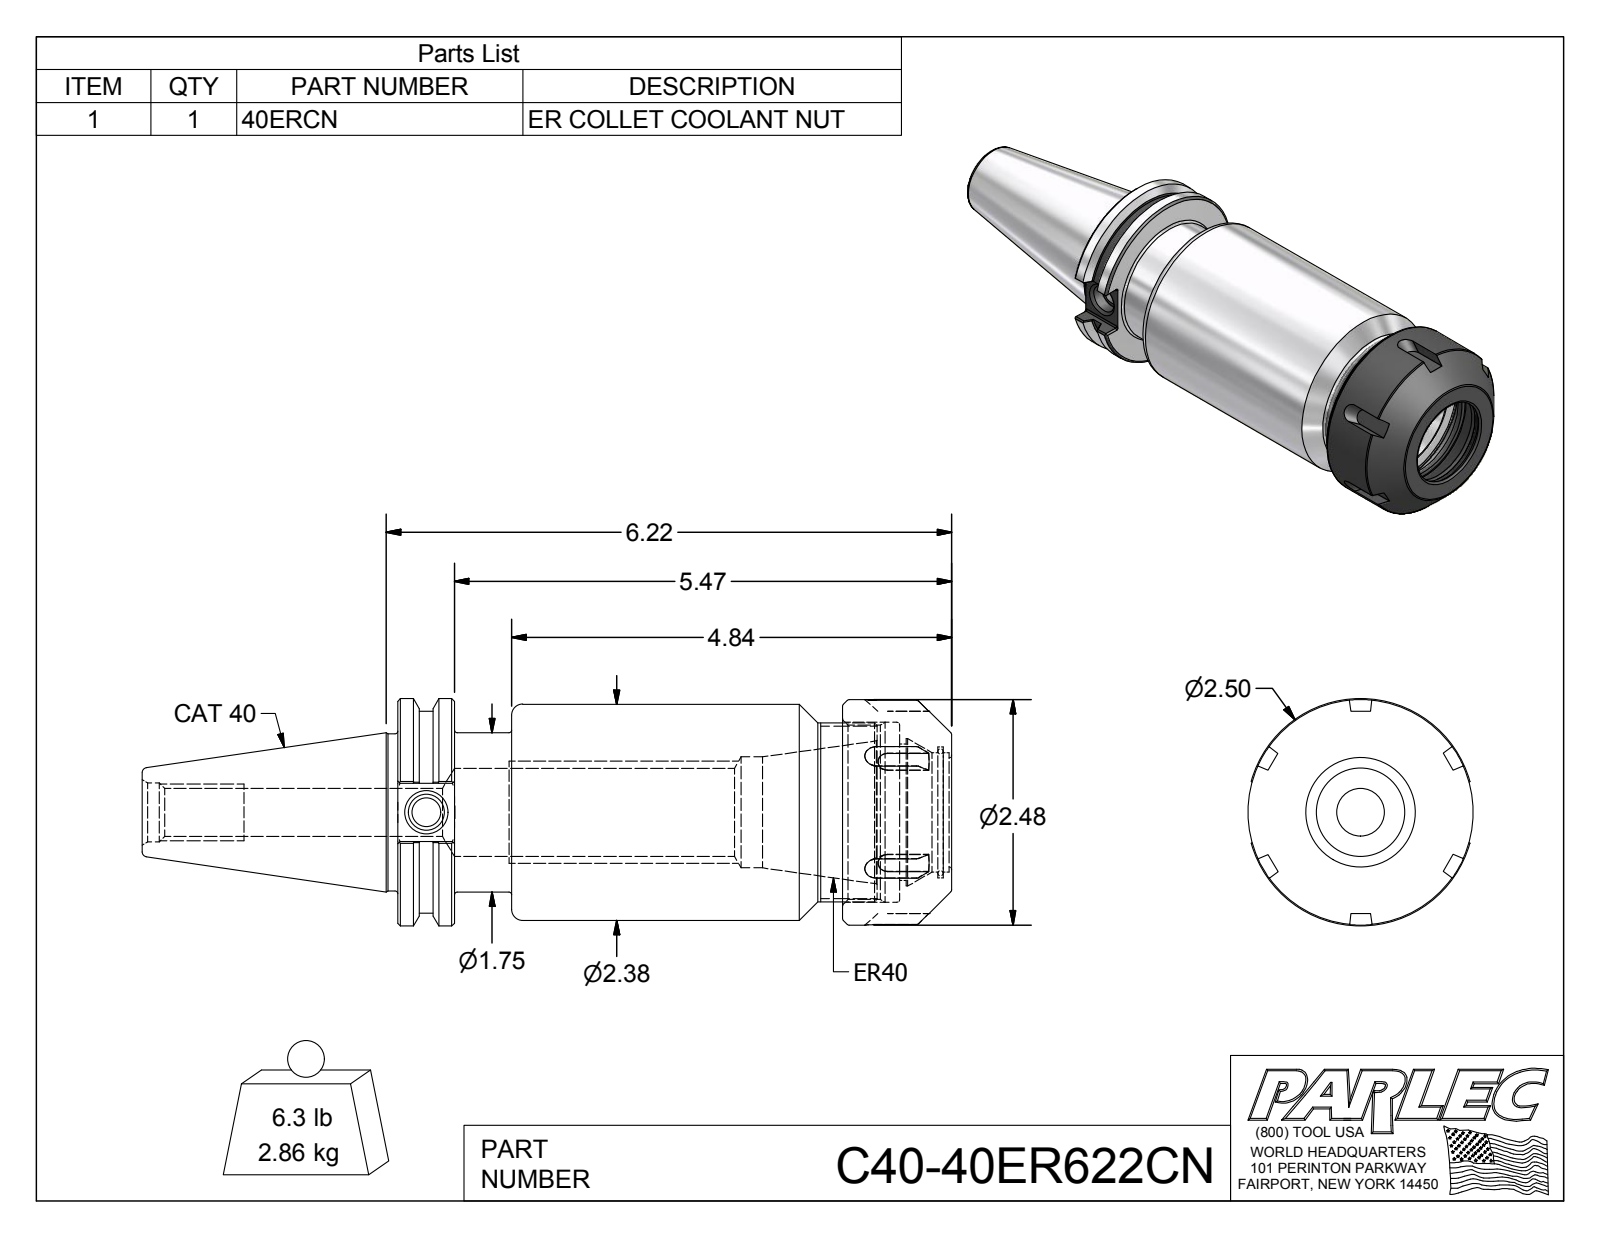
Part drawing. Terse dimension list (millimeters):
name: C40-40ER622CN; C40-40ER6-1; 40ERCN
written by: Autodesk Inventor 2012 (AUTOMOTIVE_DESIGN)
unit: mm
bodies: 2 solids, 151 faces (58 planar, 36 cylindrical, 57 other)
size: 226.2 × 63.5 × 63
volume: 364 000 mm³; area: 67 230 mm²
holes: 1× ⌀8, 1× ⌀10.1, 1× ⌀13.4, 1× ⌀16.5, 1× ⌀24.6, 1× ⌀31, 1× ⌀33.4, 1× ⌀36.5, 1× ⌀38.1, 1× ⌀41.1, 1× ⌀48.7, 1× ⌀50.3
bosses: 1× ⌀63.5, 1× ⌀63, 1× ⌀60.3, 1× ⌀56.4, 1× ⌀50, 1× ⌀44.5, 1× ⌀43.9
rounds: 12× R0.5
face distances: 15.9, 124.3, 140.2, 154.8, 138.9, 14.6, 31.9, 16, 108.3, 122.9
